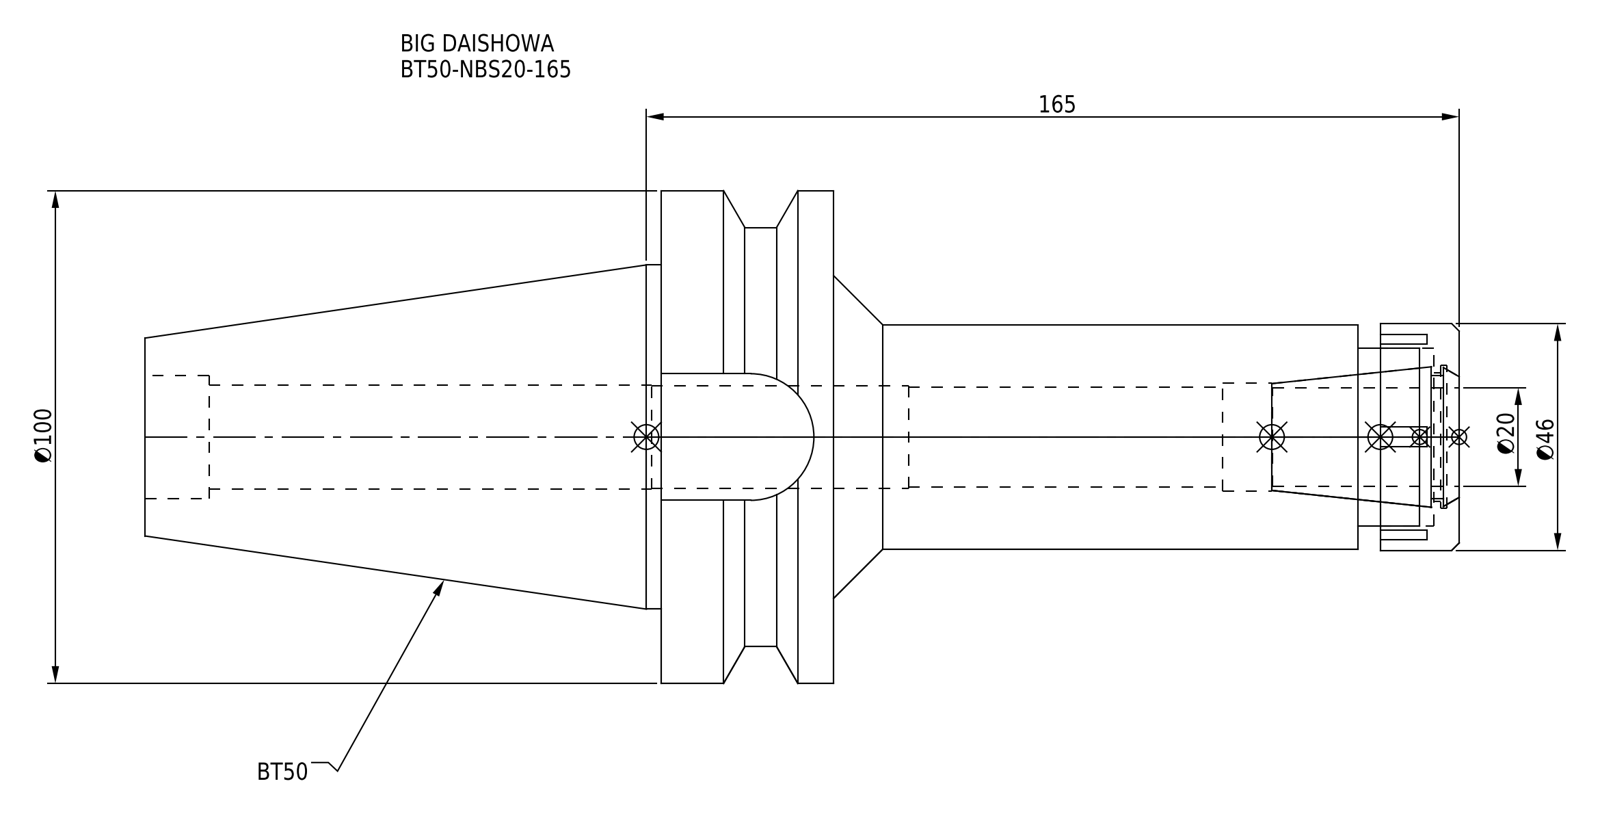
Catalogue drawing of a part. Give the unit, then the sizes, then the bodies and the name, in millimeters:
Units: millimetres
Overall size (bounding box): 266.8 × 100 × 100
Round holes (diameter × count): ⌀20.3 ×1, ⌀20.8 ×1, ⌀21.2 ×1, ⌀22 ×1, ⌀25 ×1, ⌀26 ×1, ⌀29 ×1, ⌀36 ×1
Round bosses / shafts (diameter × count): ⌀100 ×1, ⌀85 ×1, ⌀69.85 ×1, ⌀46 ×1, ⌀45.5 ×1
Partial cylindrical surfaces — rounded edges, fillets, slot ends (radius × count): R12.85 ×1
Main face-to-face distances: 35, 127, 162, 8, 266.8, 139.8, 104.8, 70.8, 20.5, 106.5
Volume: 605 072 mm³ · Surface area: 84 446 mm²
Bodies: 2 solids, 93 faces (45 planar, 34 cylindrical, 14 other)
Part name (STEP PRODUCT): BT50-NBS20-165; BT50NB20165-200_ASM.stp; BT50-NBS20-165_1.stp; DXF_TEMP_ASSY_ASM_4_ASM.stp (+3 more)
STEP written by: SolidWorks 2019 (CONFIG_CONTROL_DESIGN)
